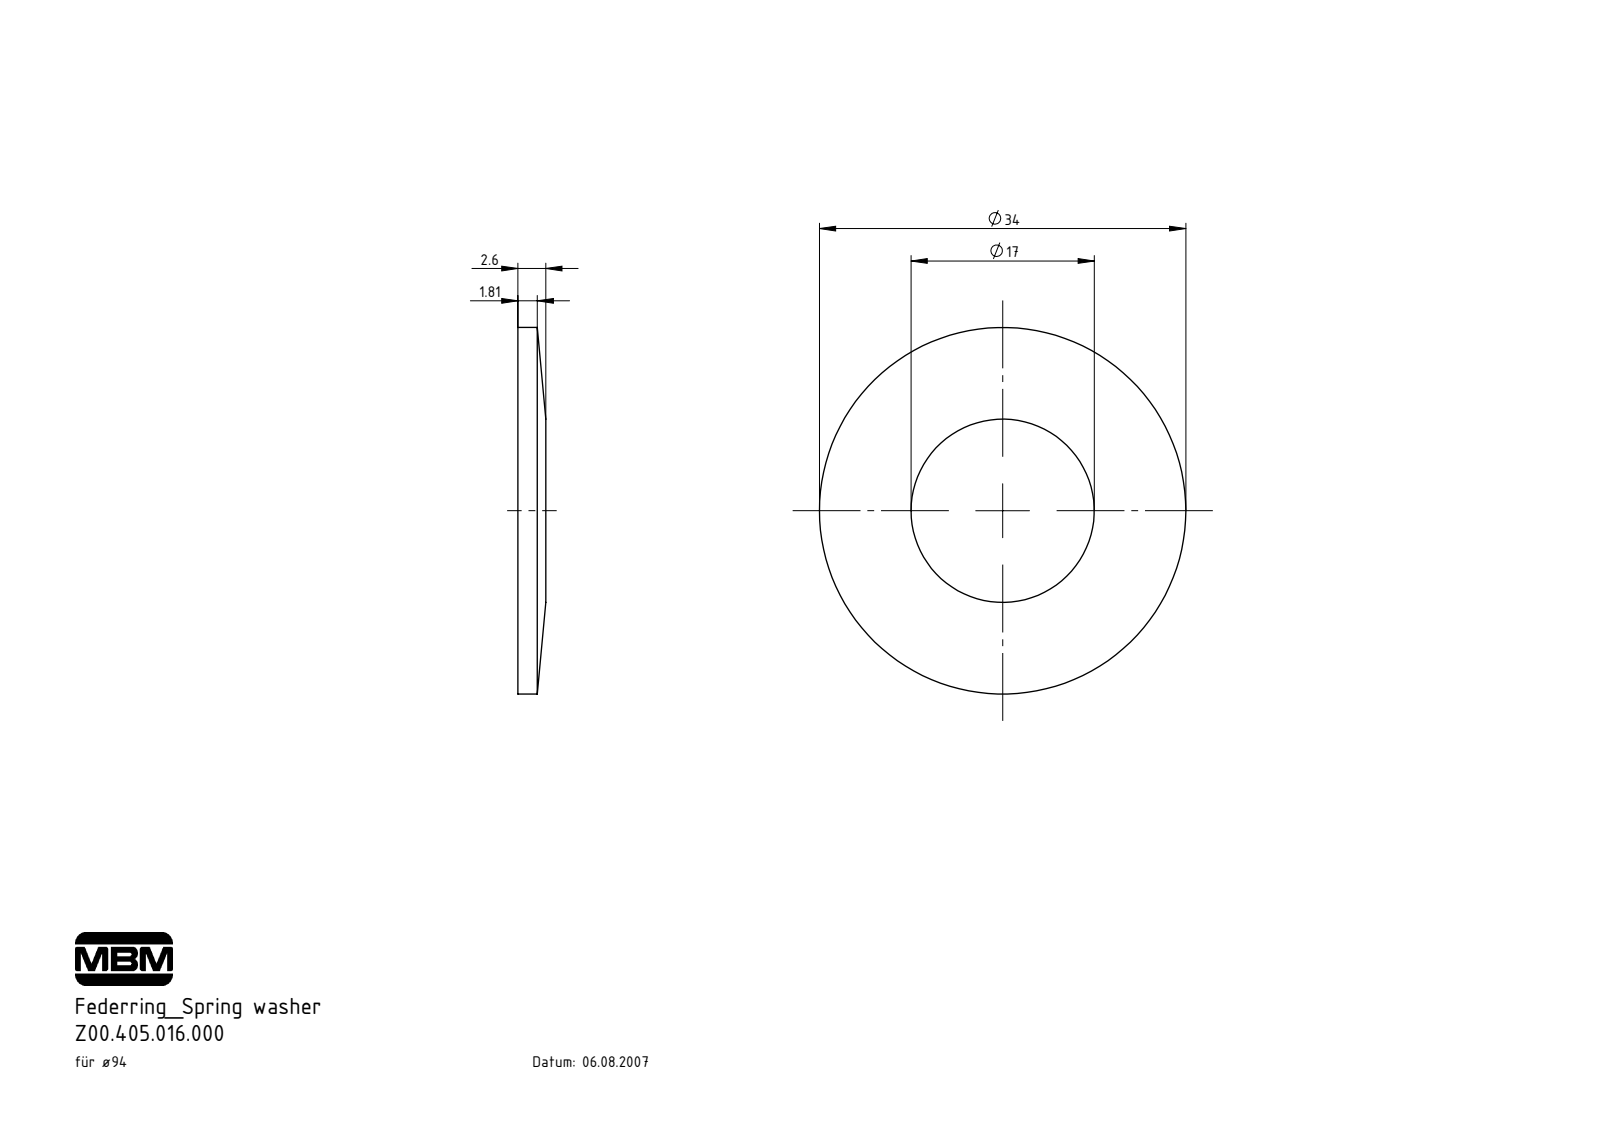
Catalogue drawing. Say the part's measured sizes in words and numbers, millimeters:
The part is named "Z00.405.016.000". Its 3-D file was written by "SolidWorks 2022 (AUTOMOTIVE_DESIGN)". It is 1 solid with 6 faces: 2 planar, 4 cylindrical and 0 other. Overall it measures 34 by 34 by 1.8 millimeters. Its volume is 1 226 cubic millimeters and its surface area 1 650 square millimeters. Round holes: 1 of diameter 17. Round bosses or shafts: 1 of diameter 34. The main face-to-face distances are 1.8.
